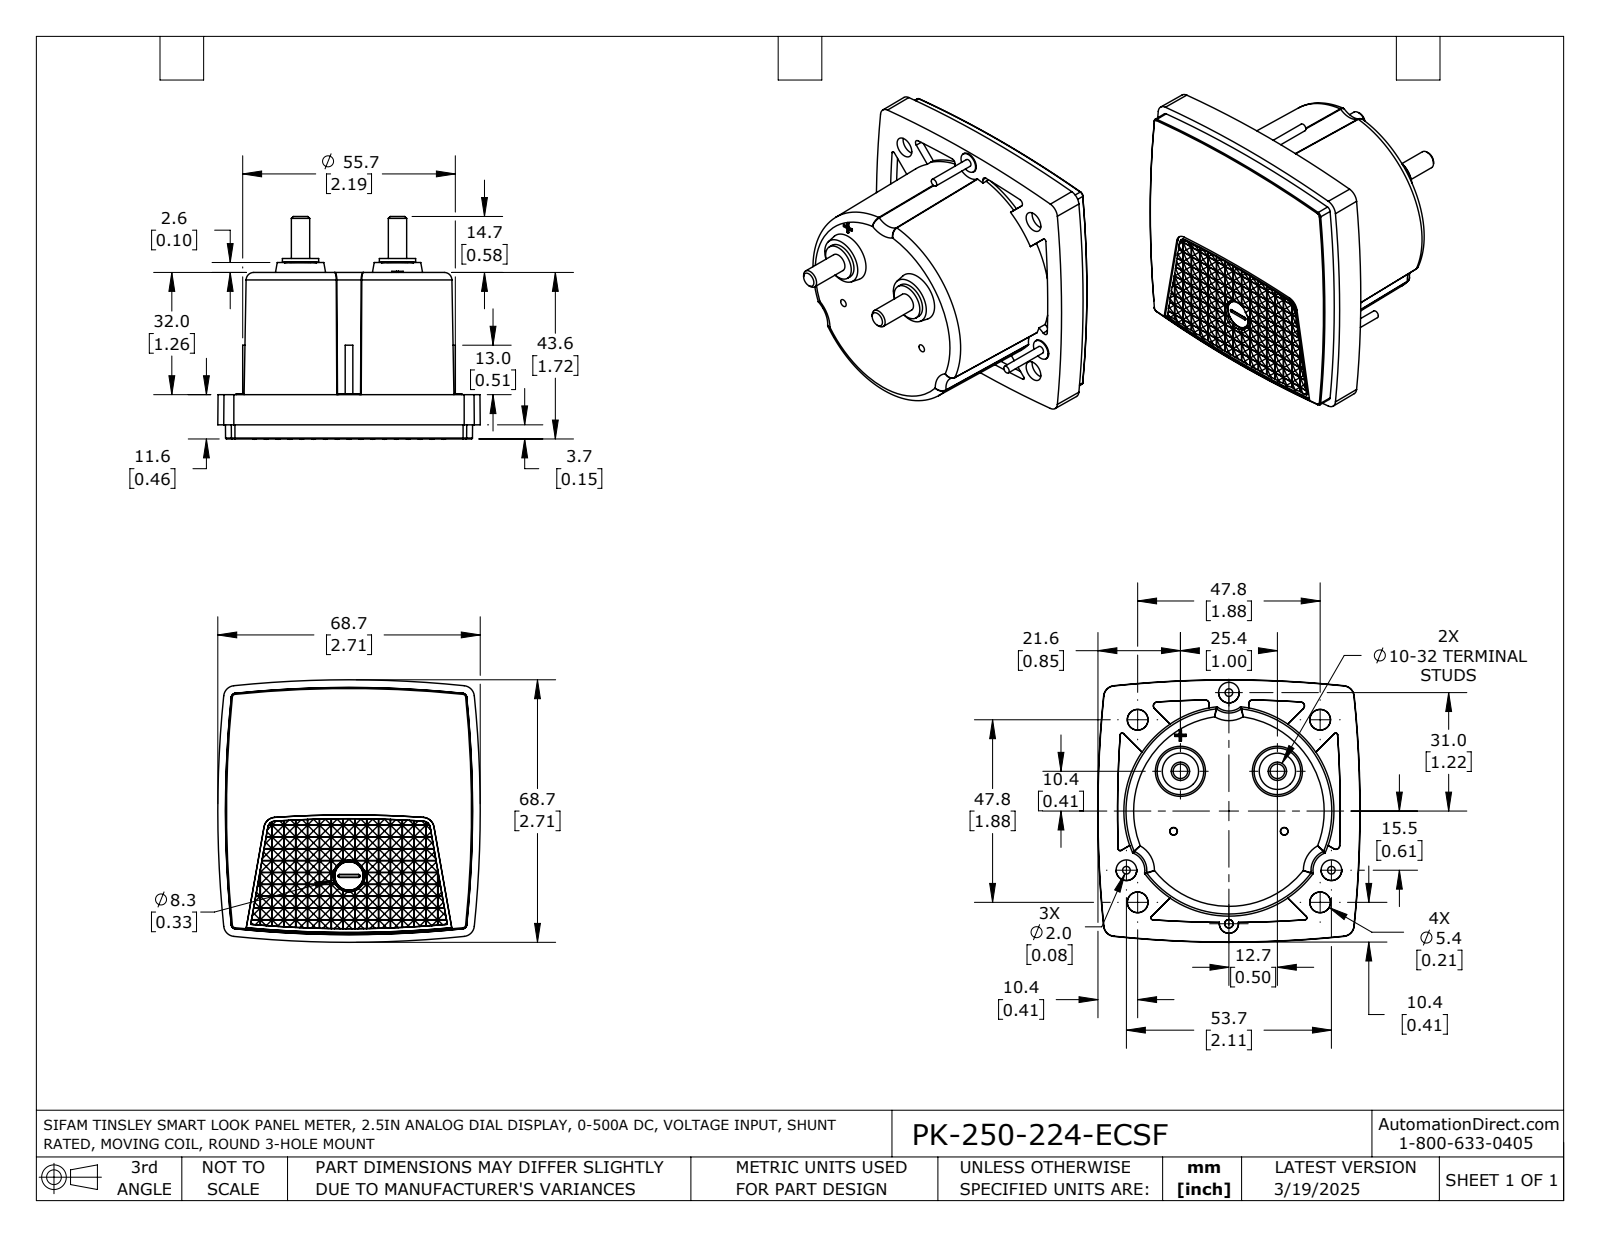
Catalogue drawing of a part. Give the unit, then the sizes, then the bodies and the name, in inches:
Units: inches
Overall size (bounding box): 2.706 × 2.706 × 2.297
Round bosses / shafts (diameter × count): ⌀0.213 ×3, ⌀0.079 ×3, ⌀0.374 ×2, ⌀0.189 ×2, ⌀0.215 ×1
Partial cylindrical surfaces — rounded edges, fillets, slot ends (radius × count): R0.167 ×2, R1.083 ×1
Main face-to-face distances: 1.717, 1.26, 0.457, 0.024, 0.087, 0.096, 0.311, 0.12, 0.072, 1.346
Volume: 7.594 in³ · Surface area: 30.41 in²
Bodies: 1 solid, 1550 faces (1165 planar, 265 cylindrical, 120 other)
Part name (STEP PRODUCT): PK-250-224-ECSF
STEP written by: SolidWorks 2021 (AUTOMOTIVE_DESIGN)
